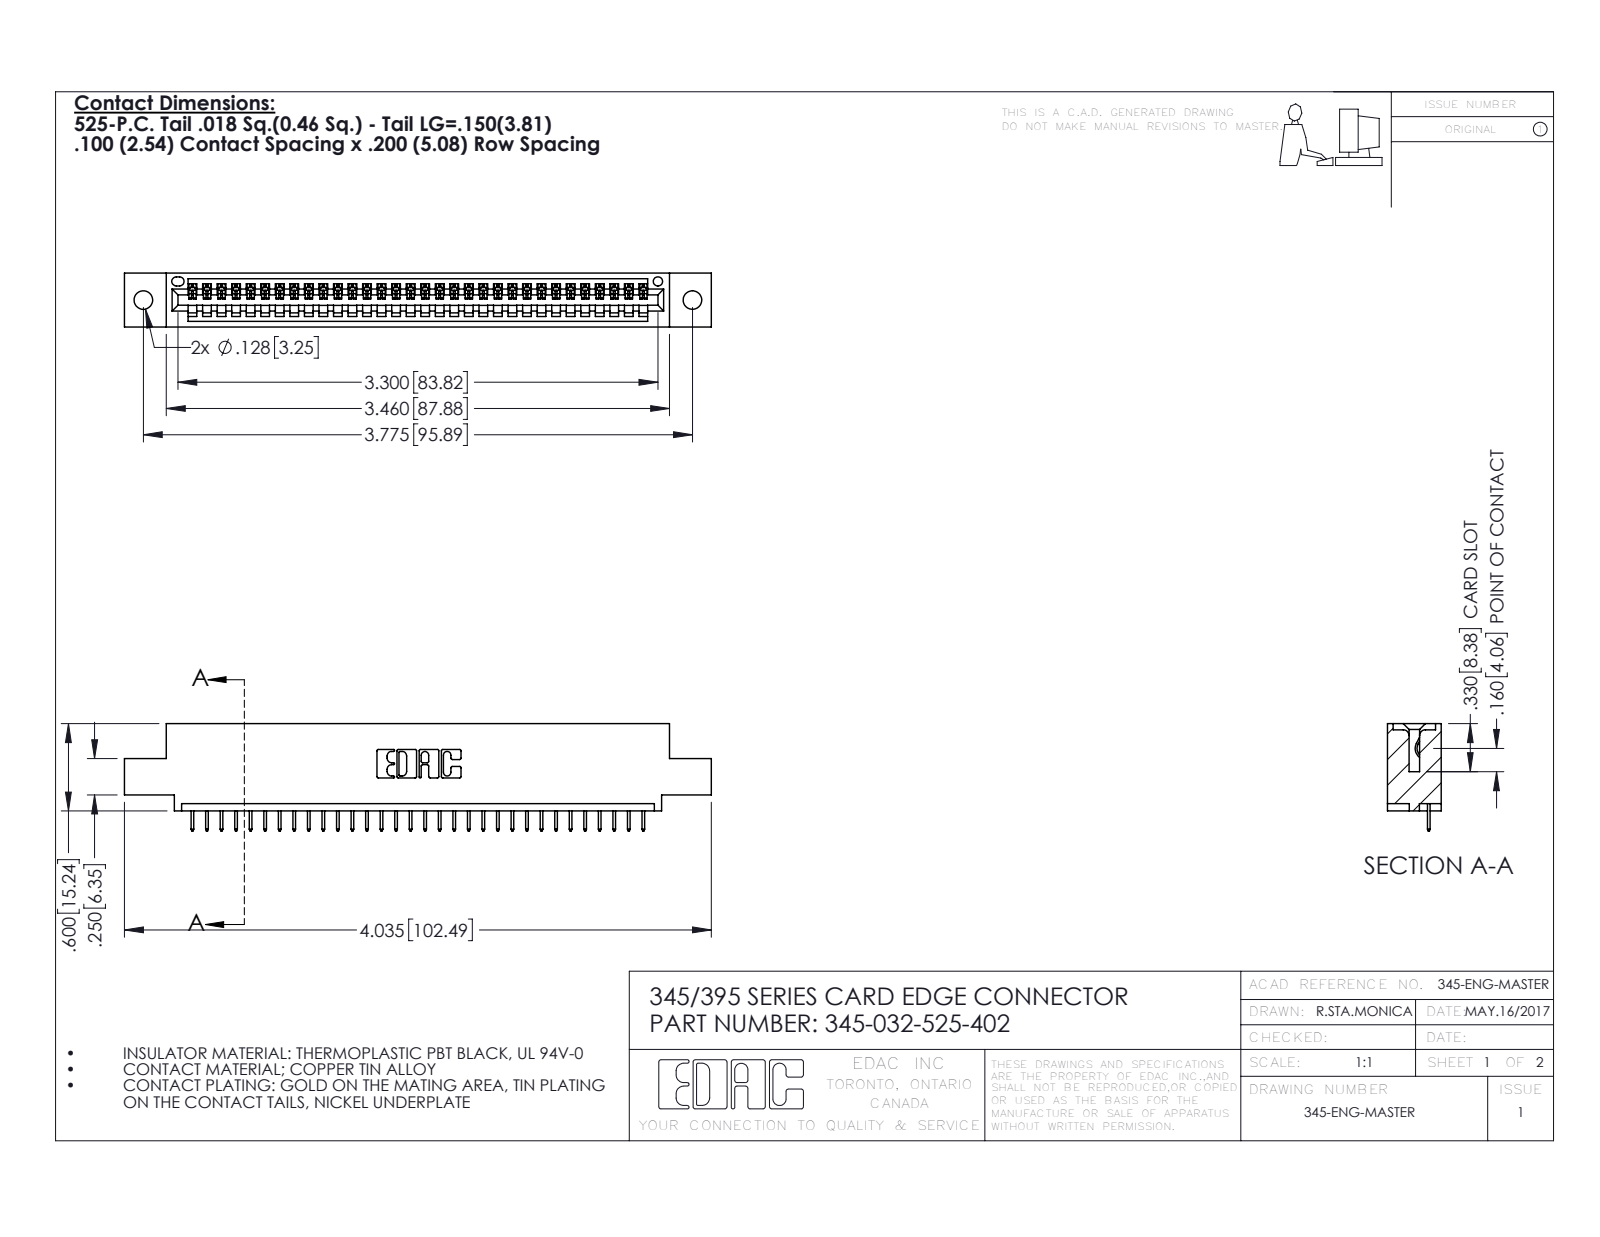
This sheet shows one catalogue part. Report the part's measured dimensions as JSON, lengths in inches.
{"part_name": "345-292-001_345-293-125; 345-032-525-402; 345 Part_0.110 Offset - 0.128 Dia", "step_written_by": "SolidWorks 2020 (CONFIG_CONTROL_DESIGN)", "units": "inches", "bodies": {"solids": 33, "faces": 2114, "planar": 1556, "cylindrical": 558, "other": 0}, "overall_size": [4.035, 0.737, 0.37], "volume_in3": 0.574, "surface_area_in2": 18.21, "round_holes": [[0.128, 2], [0.064, 1]], "partial_cylinders_radius": [[0.006, 64], [0.01, 22], [0.007, 6], [0.031, 6], [0.026, 3], [0.031, 2], [0.04, 2], [0.014, 1]], "face_to_face_distances": [0.072, 0.298, 0.37, 0.2, 0.098, 0.272, 0.025, 0.225, 0.072, 0.149], "hole_center_spacings": [0.27, 3.54, 3.775]}
